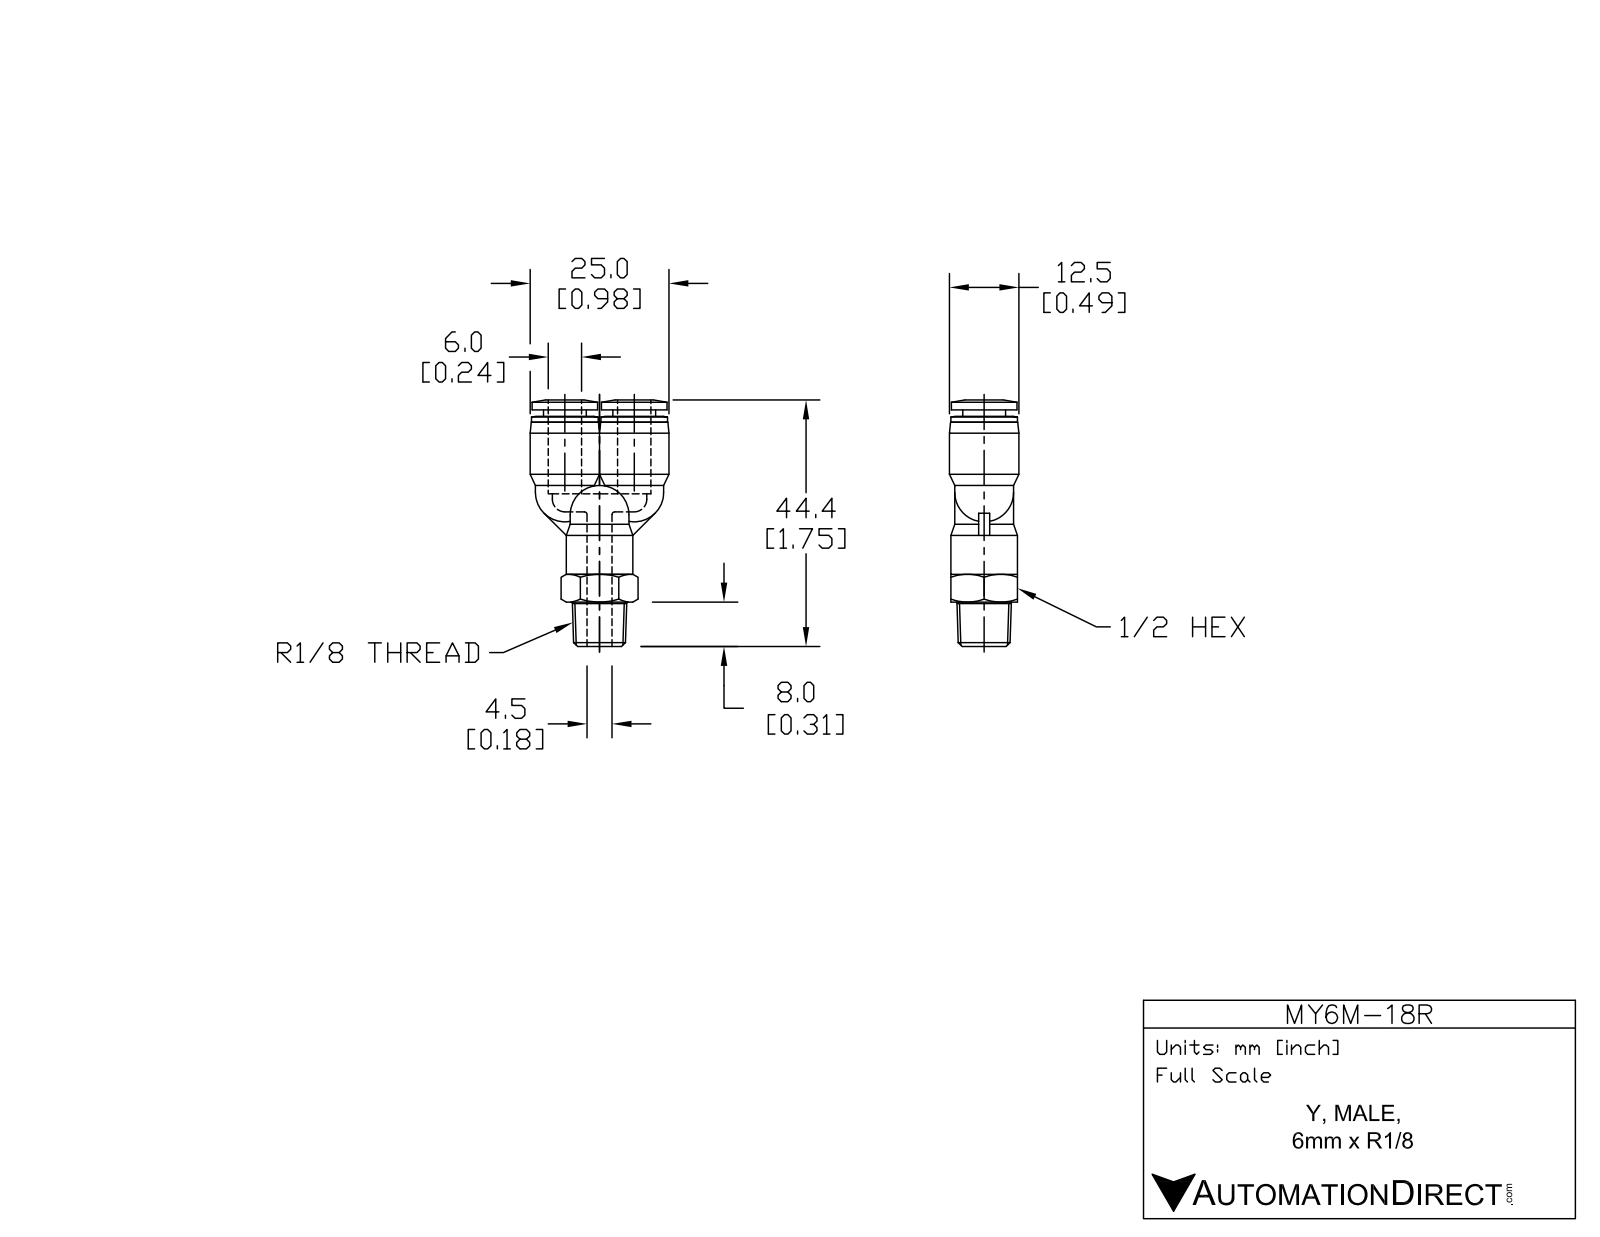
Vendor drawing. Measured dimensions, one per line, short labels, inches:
name: MY6M-18R
written by: SolidWorks 2015 (AUTOMOTIVE_DESIGN)
unit: in
bodies: 1 solid, 101 faces (23 planar, 34 cylindrical, 44 other)
size: 1.748 × 0.984 × 0.492
volume: 0.319 in³; area: 6.255 in²
holes: 4× ⌀0.157, 2× ⌀0.248
bosses: 3× ⌀0.472, 3× ⌀0.417, 2× ⌀0.492, 2× ⌀0.465, 2× ⌀0.303
face distances: 0.472, 0.045, 1.317, 1.362, 0.768, 0.549, 0.594, 0.315, 1.083, 1.632
hole spacings: 0.246, 0.492
